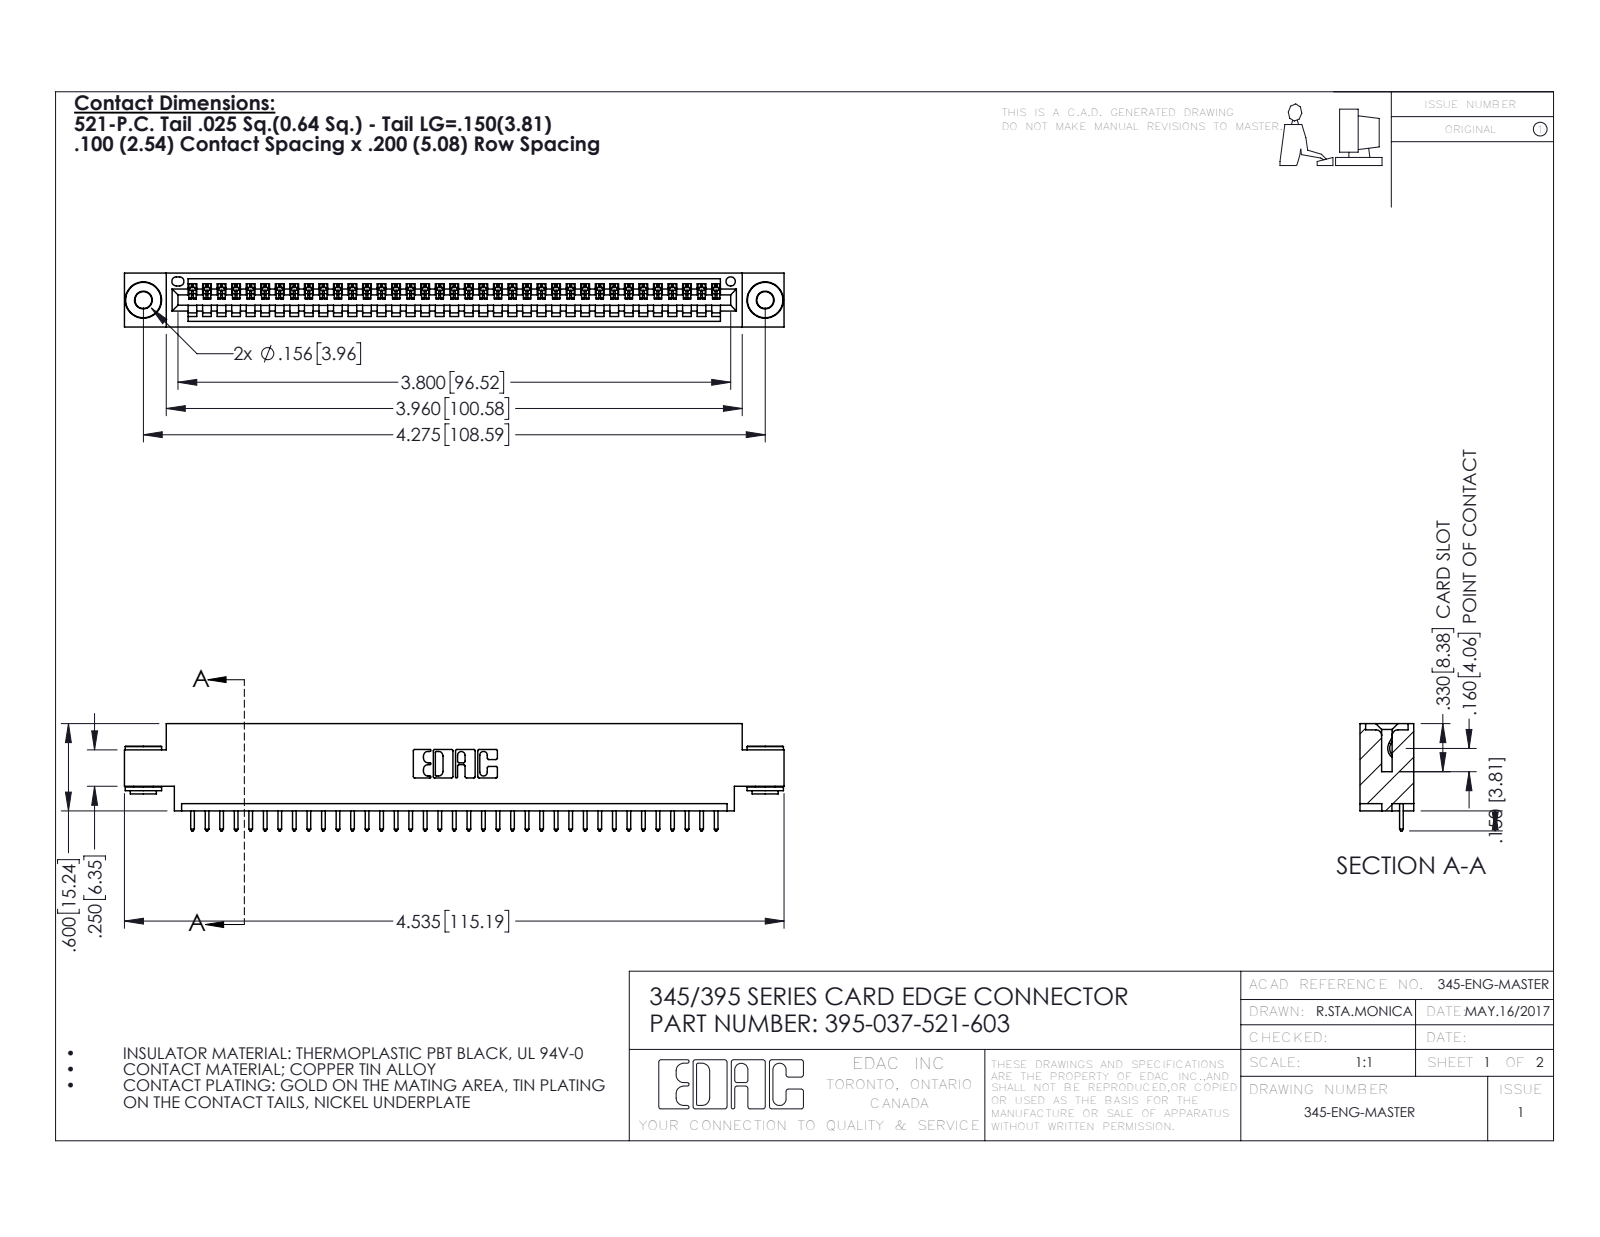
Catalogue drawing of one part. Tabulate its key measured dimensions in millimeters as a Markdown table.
| quantity | value |
| --- | --- |
| part name | 395-037-521-603; 345 Part_0.170 Offset - 0.156 Dia-TH; 345-250-002_345-250-002-102; 345-292-001_345-293-121 |
| STEP written by | SolidWorks 2016 (CONFIG_CONTROL_DESIGN) |
| units | millimeters |
| bodies | 40 solids, 2314 faces (1574 planar, 732 cylindrical, 8 other) |
| overall size | 115.2 × 18.7 × 9.4 |
| volume | 10 700 mm³ |
| surface area | 14 080 mm² |
| round holes (diameter × count) | 2.9 × 2, 4 × 2, 1.6 × 1 |
| round bosses / shafts (diameter × count) | 6.4 × 2, 4.6 × 2, 3.5 × 2 |
| partial cylindrical surfaces (radius × count) | 0.2 × 74, 0.3 × 74, 0.3 × 22, 0.2 × 6, 0.8 × 6, 0.7 × 3, 0.8 × 2, 1 × 2 |
| main face-to-face distances | 1.8, 7.6, 9.4, 5.1, 2.5, 6.9, 0.6, 5.7, 4.4, 3.8 |
| hole center spacings | 6.9, 102.6, 108.6 |
